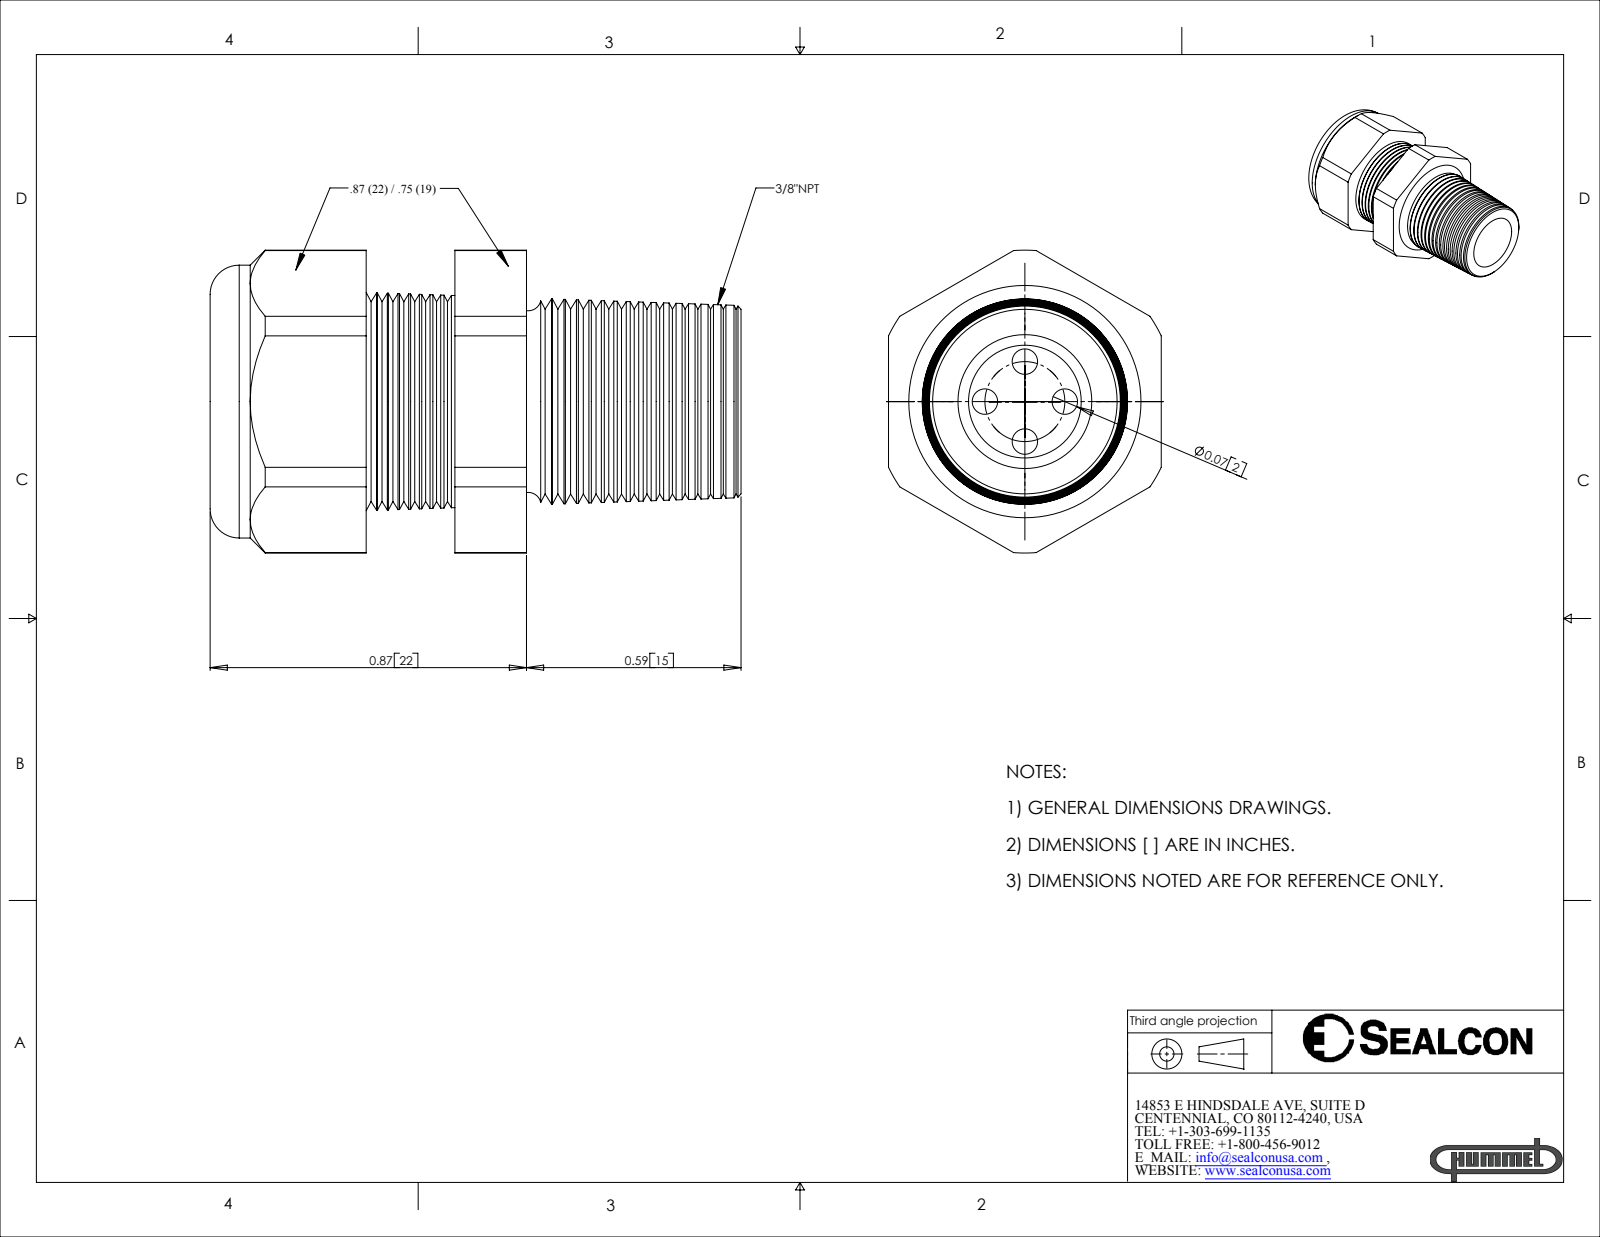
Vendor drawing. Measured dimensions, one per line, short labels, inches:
name: CD09N8-BK
written by: SolidWorks 2007 (CONFIG_CONTROL_DESIGN)
unit: in
bodies: 2 solids, 206 faces (20 planar, 28 cylindrical, 158 other)
size: 1.46 × 0.833 × 0.75
volume: 0.368 in³; area: 7.041 in²
holes: 4× ⌀0.07, 1× ⌀0.29, 1× ⌀0.31
bosses: 1× ⌀0.75
rounds: 1× R0.416
face distances: 0.75, 0.673, 0.429, 0.244, 0.75, 0.87, 0.441, 0.197, 1.46, 1.031
hole spacings: 0.11, 0.156, 0.22
